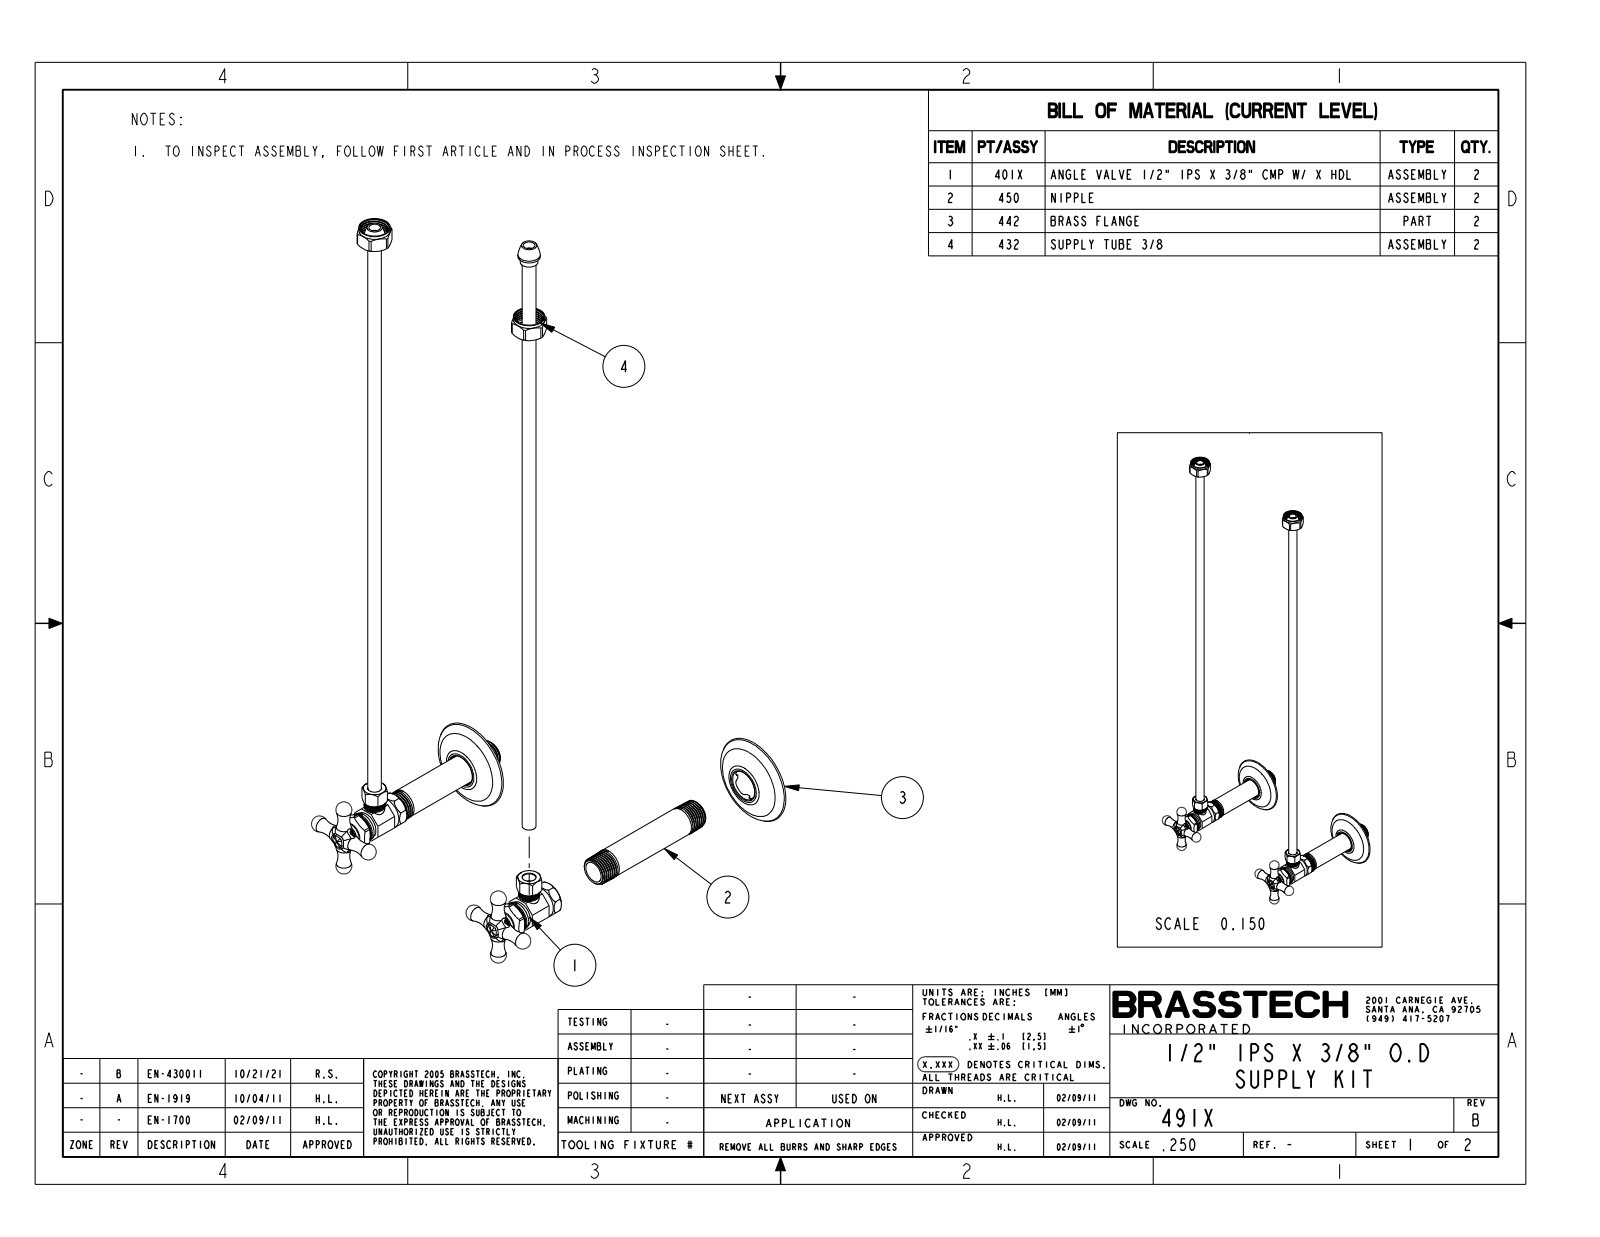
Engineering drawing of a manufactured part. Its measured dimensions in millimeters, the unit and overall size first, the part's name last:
Units: millimetres
Overall size (bounding box): 538.7 × 215.9 × 152.1
Round holes (diameter × count): ⌀3.3 ×2, ⌀8.1 ×2, ⌀9.5 ×2, ⌀9.6 ×2, ⌀10 ×2, ⌀10.2 ×2, ⌀11.8 ×2, ⌀12.2 ×2, ⌀13.2 ×2, ⌀14.3 ×2, ⌀15.1 ×2, ⌀16.6 ×2
Round bosses / shafts (diameter × count): ⌀21.8 ×2, ⌀20.6 ×2, ⌀19.1 ×2, ⌀17.3 ×2, ⌀17.2 ×2, ⌀16 ×2, ⌀15.8 ×2, ⌀15.7 ×2
Partial cylindrical surfaces — rounded edges, fillets, slot ends (radius × count): R0.3 ×36, R1.3 ×12, R3.8 ×6, R4.3 ×2, R6.5 ×2, R9.6 ×2, R12.4 ×2, R4.8 ×1
Main face-to-face distances: 22.2, 132, 22.9, 15.9, 76.2, 2.5, 152.4, 109.8, 154.2, 2.2
Hole centre spacings: 152.4, 107.8
Volume: 67 830 mm³ · Surface area: 187 900 mm²
Bodies: 8 solids, 1714 faces (426 planar, 624 cylindrical, 664 other)
Part name (STEP PRODUCT): 491X
STEP written by: CREO PARAMETRIC BY PTC INC, 2018500 (CONFIG_CONTROL_DESIGN)
